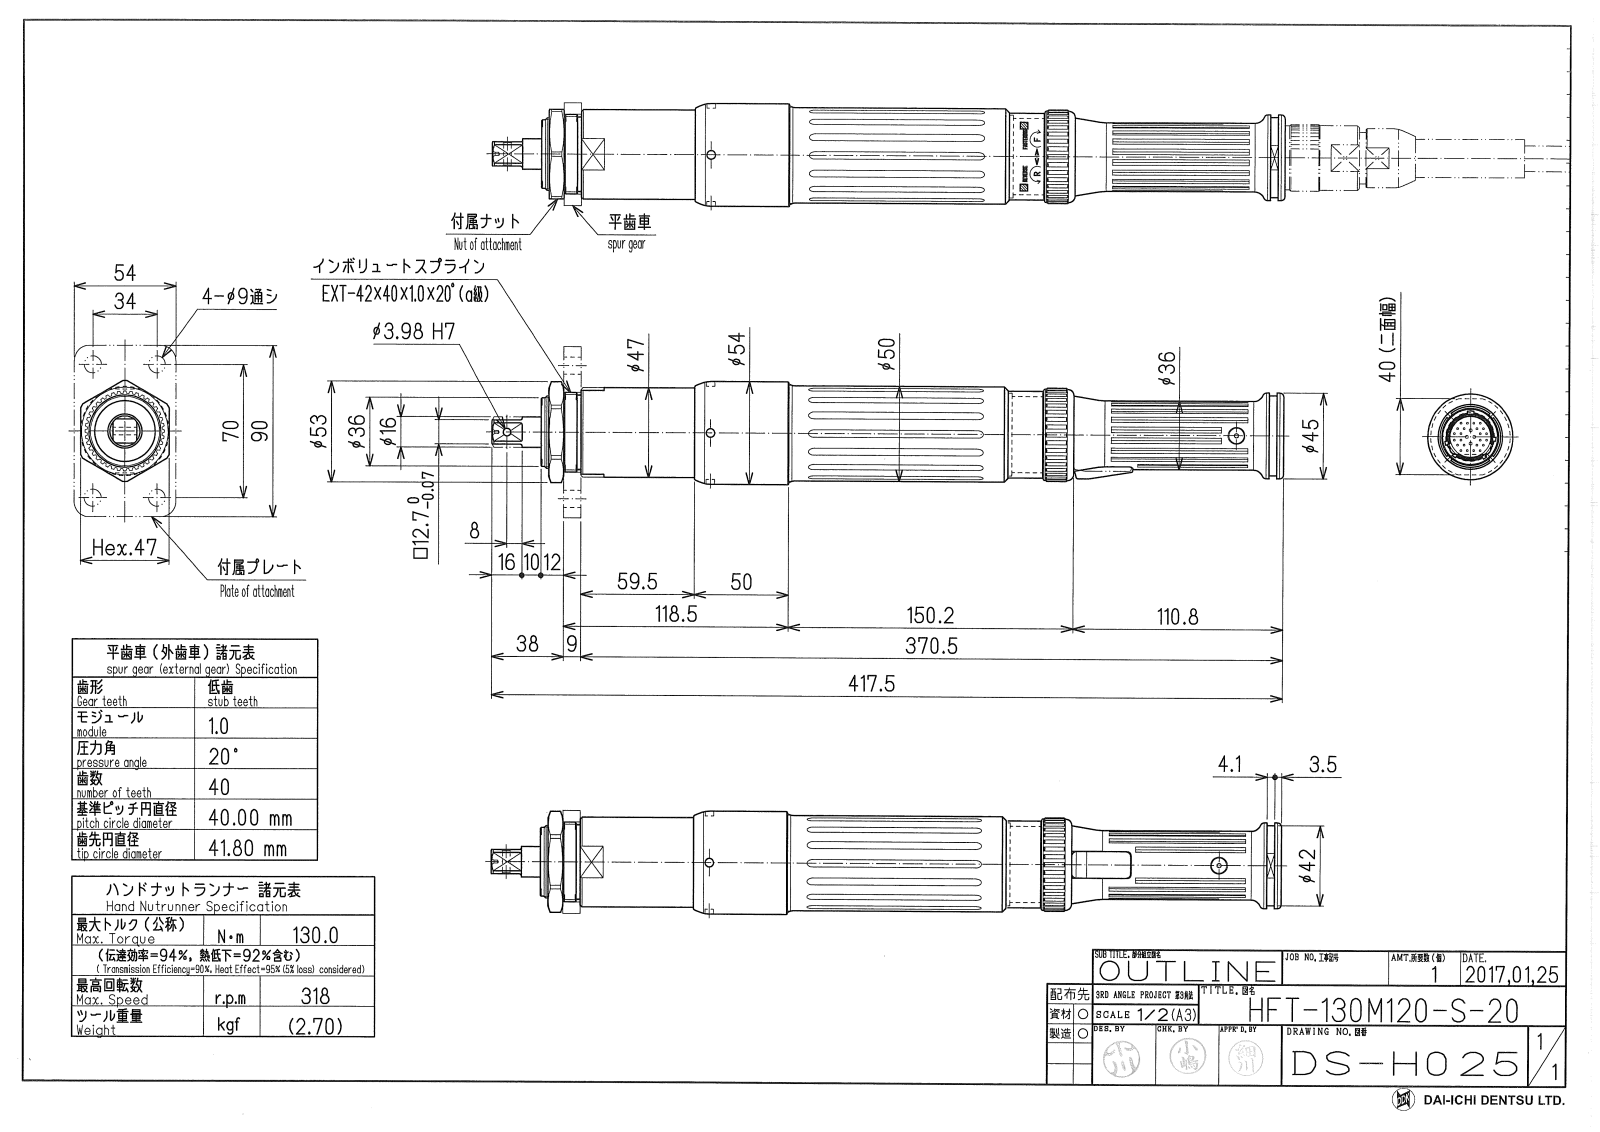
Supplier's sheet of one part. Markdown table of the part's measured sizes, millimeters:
| quantity | value |
| --- | --- |
| part name | HFT-130M120-S-20(DS-H025)_OUTLINE |
| STEP written by | Autodesk Inventor 2017 (AUTOMOTIVE_DESIGN) |
| units | millimeters |
| bodies | 1 solid, 826 faces (444 planar, 257 cylindrical, 125 other) |
| overall size | 417.5 × 90 × 54 |
| volume | 671 667 mm³ |
| surface area | 79 250 mm² |
| round holes (diameter × count) | 9 × 6, 4.6 × 2, 3.98 × 1, 4.5 × 1, 6.8 × 1, 22.6 × 1, 25 × 1, 25.8 × 1, 26.7 × 1, 34 × 1, 41.2 × 1, 52.4 × 1 |
| round bosses / shafts (diameter × count) | 1 × 24, 1.6 × 4, 8 × 2, 4 × 2, 54 × 1, 52 × 1, 50 × 1, 48 × 1 |
| partial cylindrical surfaces (radius × count) | 0.1 × 36, 1.5 × 36, 3 × 19, 0.33 × 18, 1 × 6, 2.5 × 6, 8 × 4, 0.3 × 2 |
| main face-to-face distances | 9, 34.96, 47, 54, 8, 17, 388.5, 1, 372.1, 49 |
| hole center spacings | 38.91, 34, 70, 77.82, 107, 269.5, 277.5, 384.5 |
